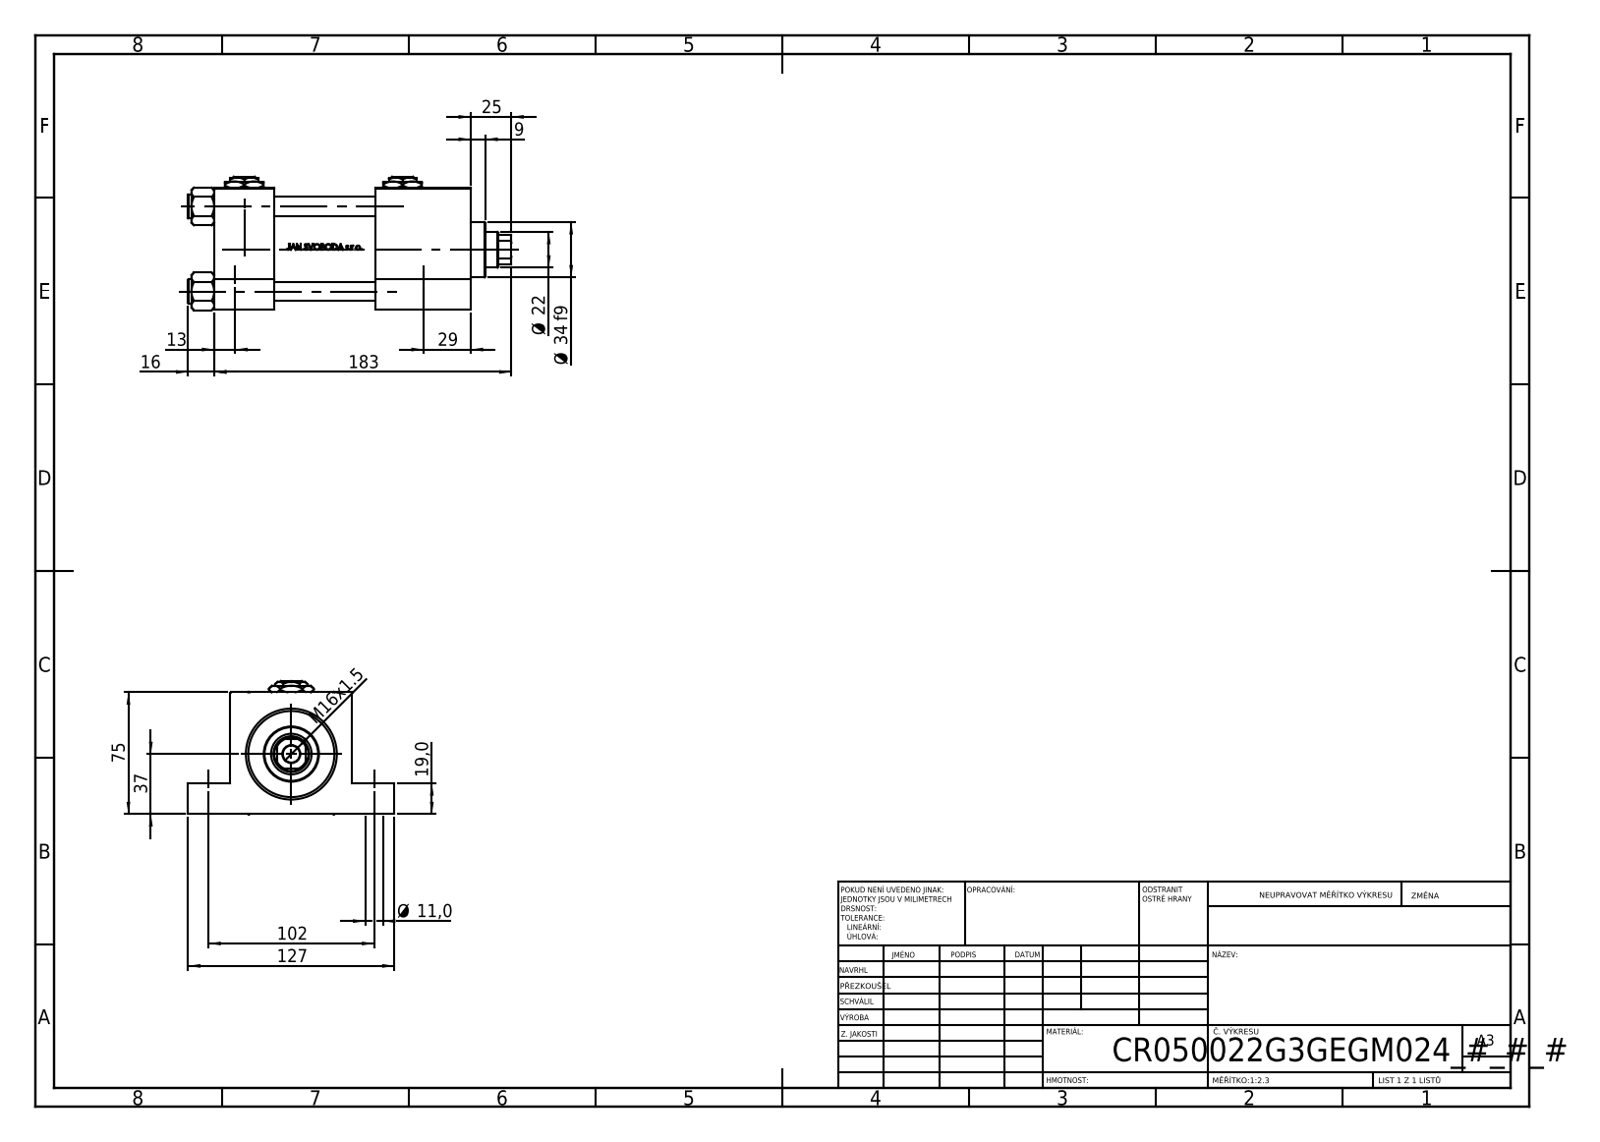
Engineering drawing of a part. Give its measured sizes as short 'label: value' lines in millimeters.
name: V215CR_G_Body; V215_VC_A; Zatka_pro_OIL_PORT; V215CR_G_TYCINKA (+2 more)
written by: SolidWorks 2019 (CONFIG_CONTROL_DESIGN)
unit: mm
bodies: 13 solids, 1172 faces (476 planar, 124 cylindrical, 572 other)
size: 199 × 127 × 82.27
volume: 766 552 mm³; area: 164 504 mm²
holes: 4× ⌀11, 4× ⌀12, 2× ⌀7, 2× ⌀20.96, 2× ⌀30, 1× ⌀10.5, 1× ⌀22, 1× ⌀25, 1× ⌀41, 1× ⌀50, 1× ⌀53
bosses: 4× ⌀15, 1× ⌀56, 1× ⌀34
rounds: 1× R10.5
face distances: 75, 37, 158, 121, 19, 56, 99, 62, 59, 26
hole spacings: 52.3, 36.63, 37.34, 51.3, 52.63, 73.96, 102, 114.93
